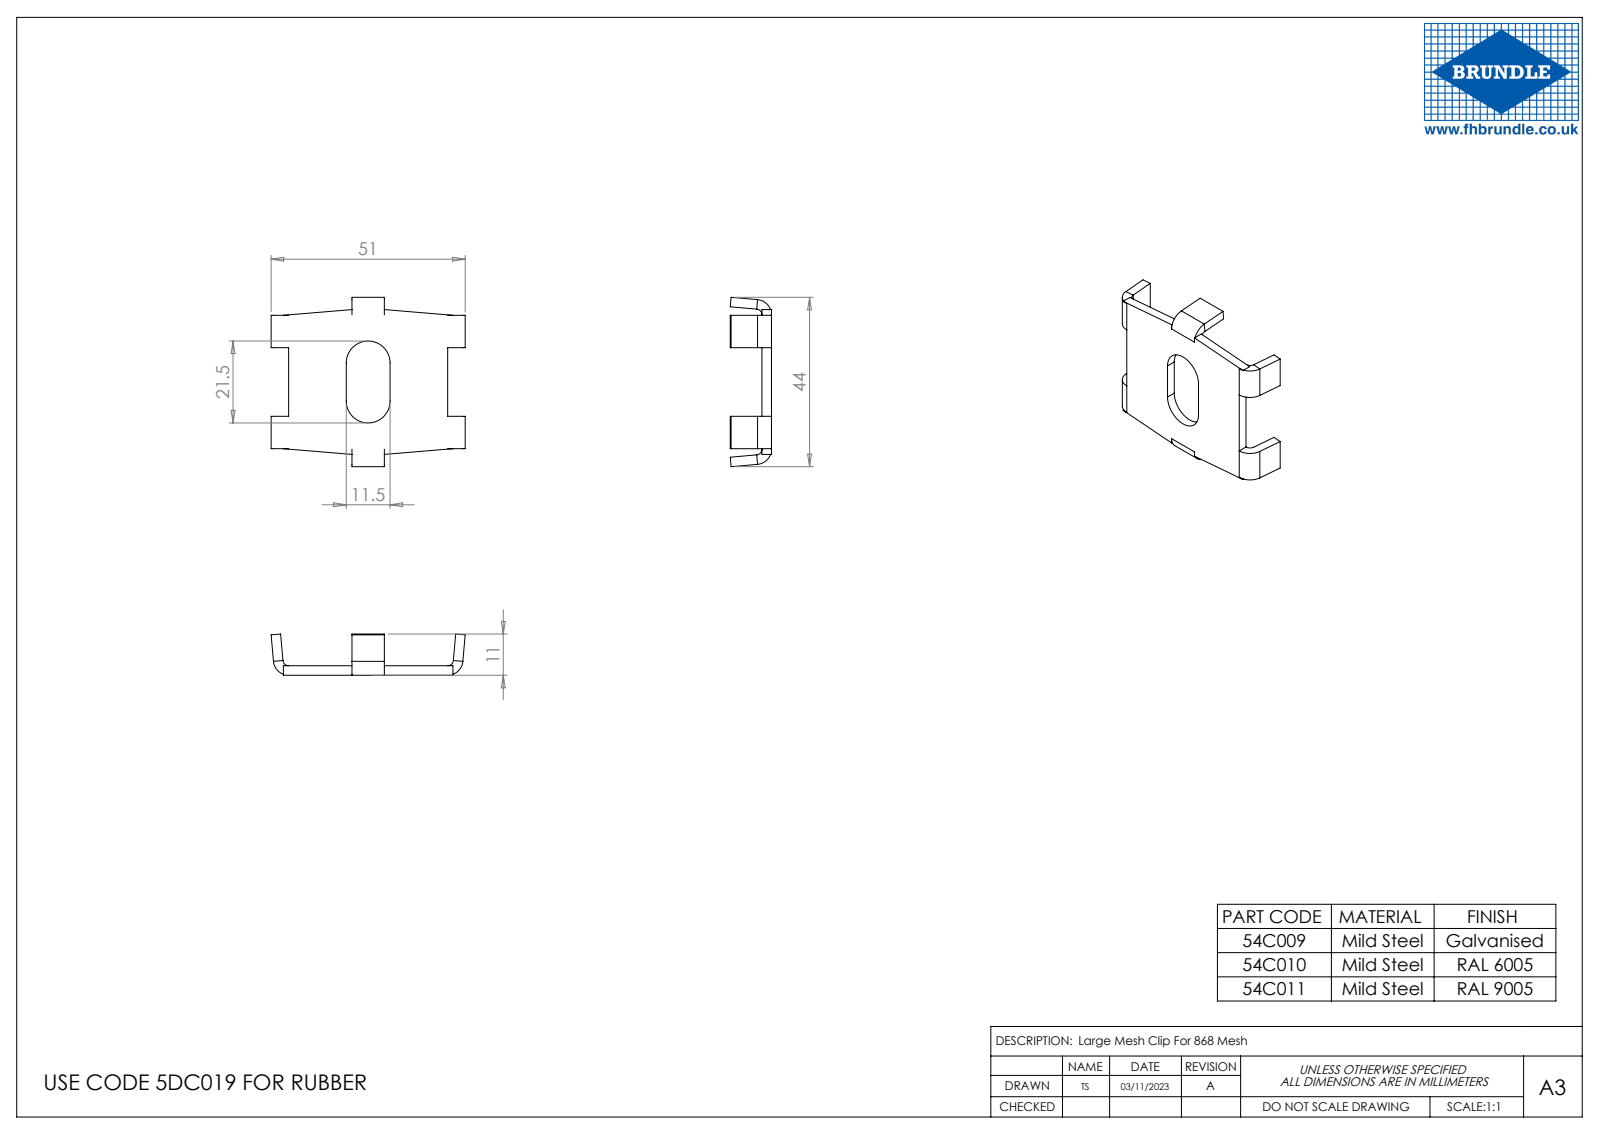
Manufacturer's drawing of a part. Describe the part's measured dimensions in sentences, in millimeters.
The part is named "54C009". Its 3-D file was written by "SolidWorks 2023 (CONFIG_CONTROL_DESIGN)". It is 1 solid with 70 faces: 56 planar, 14 cylindrical and 0 other. Overall it measures 50.94 by 44.44 by 10.82 millimeters. Its volume is 4 656 cubic millimeters and its surface area 4 569 square millimeters. Partial cylindrical surfaces (rounded edges, fillets, slot ends): 4 of radius 1.5, 4 of radius 4, 2 of radius 5.75. The main face-to-face distances are 2.5, 8.5, 26.5, 38.59, 16.63, 25.13, 18, 15.13, 26.63, 1.5.
